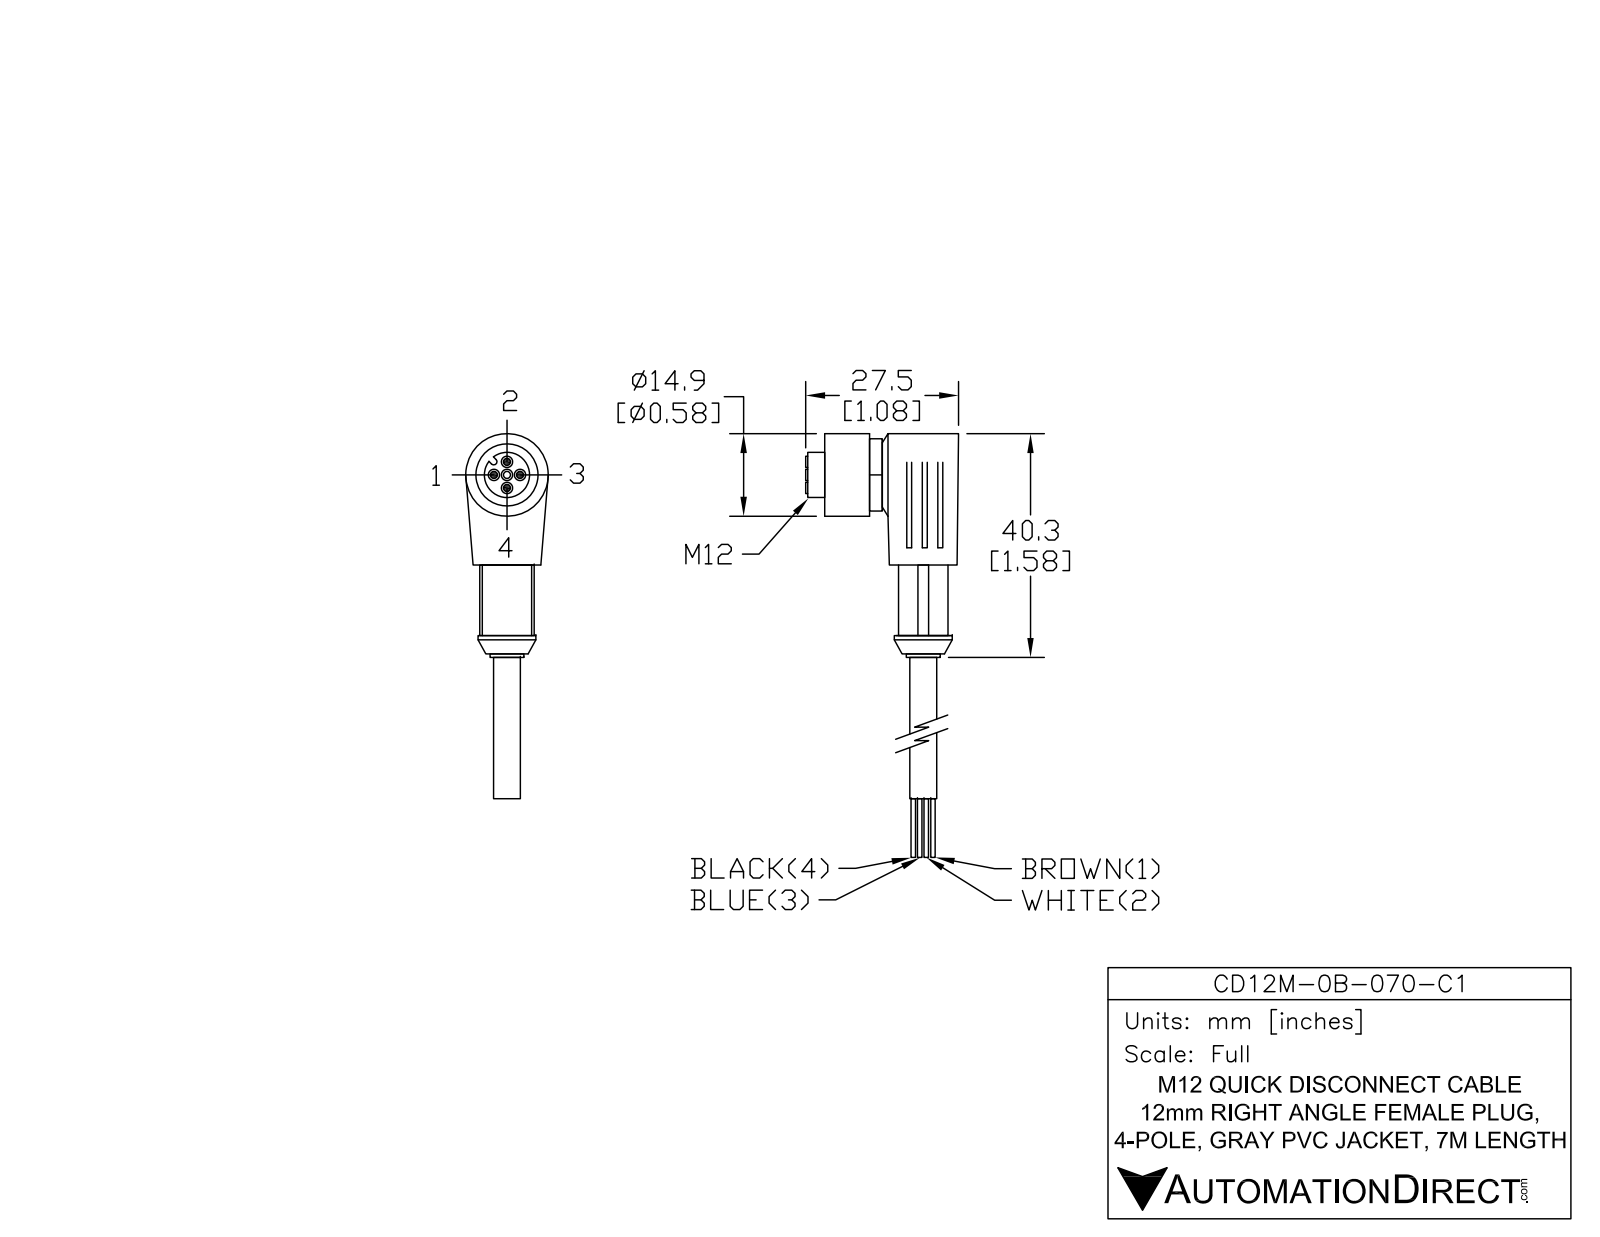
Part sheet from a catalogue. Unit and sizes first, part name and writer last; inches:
Units: inches
Overall size (bounding box): 5.524 × 1.083 × 0.587
Round holes (diameter × count): ⌀0.039 ×5, ⌀0.335 ×1, ⌀0.472 ×1
Round bosses / shafts (diameter × count): ⌀0.587 ×1, ⌀0.409 ×1, ⌀0.343 ×1, ⌀0.319 ×1, ⌀0.193 ×1
Partial cylindrical surfaces — rounded edges, fillets, slot ends (radius × count): R0.022 ×1
Main face-to-face distances: 0.539, 0.5, 0.039, 0.055, 0.594, 0.094, 0.657, 0.232, 1.008, 0.508
Hole centre spacings: 0.093, 0.131, 0.185
Volume: 0.52 in³ · Surface area: 8.517 in²
Bodies: 4 solids, 326 faces (218 planar, 106 cylindrical, 2 other)
Part name (STEP PRODUCT): CD12M-0B-070-C1
STEP written by: SolidWorks 2017 (AUTOMOTIVE_DESIGN)
